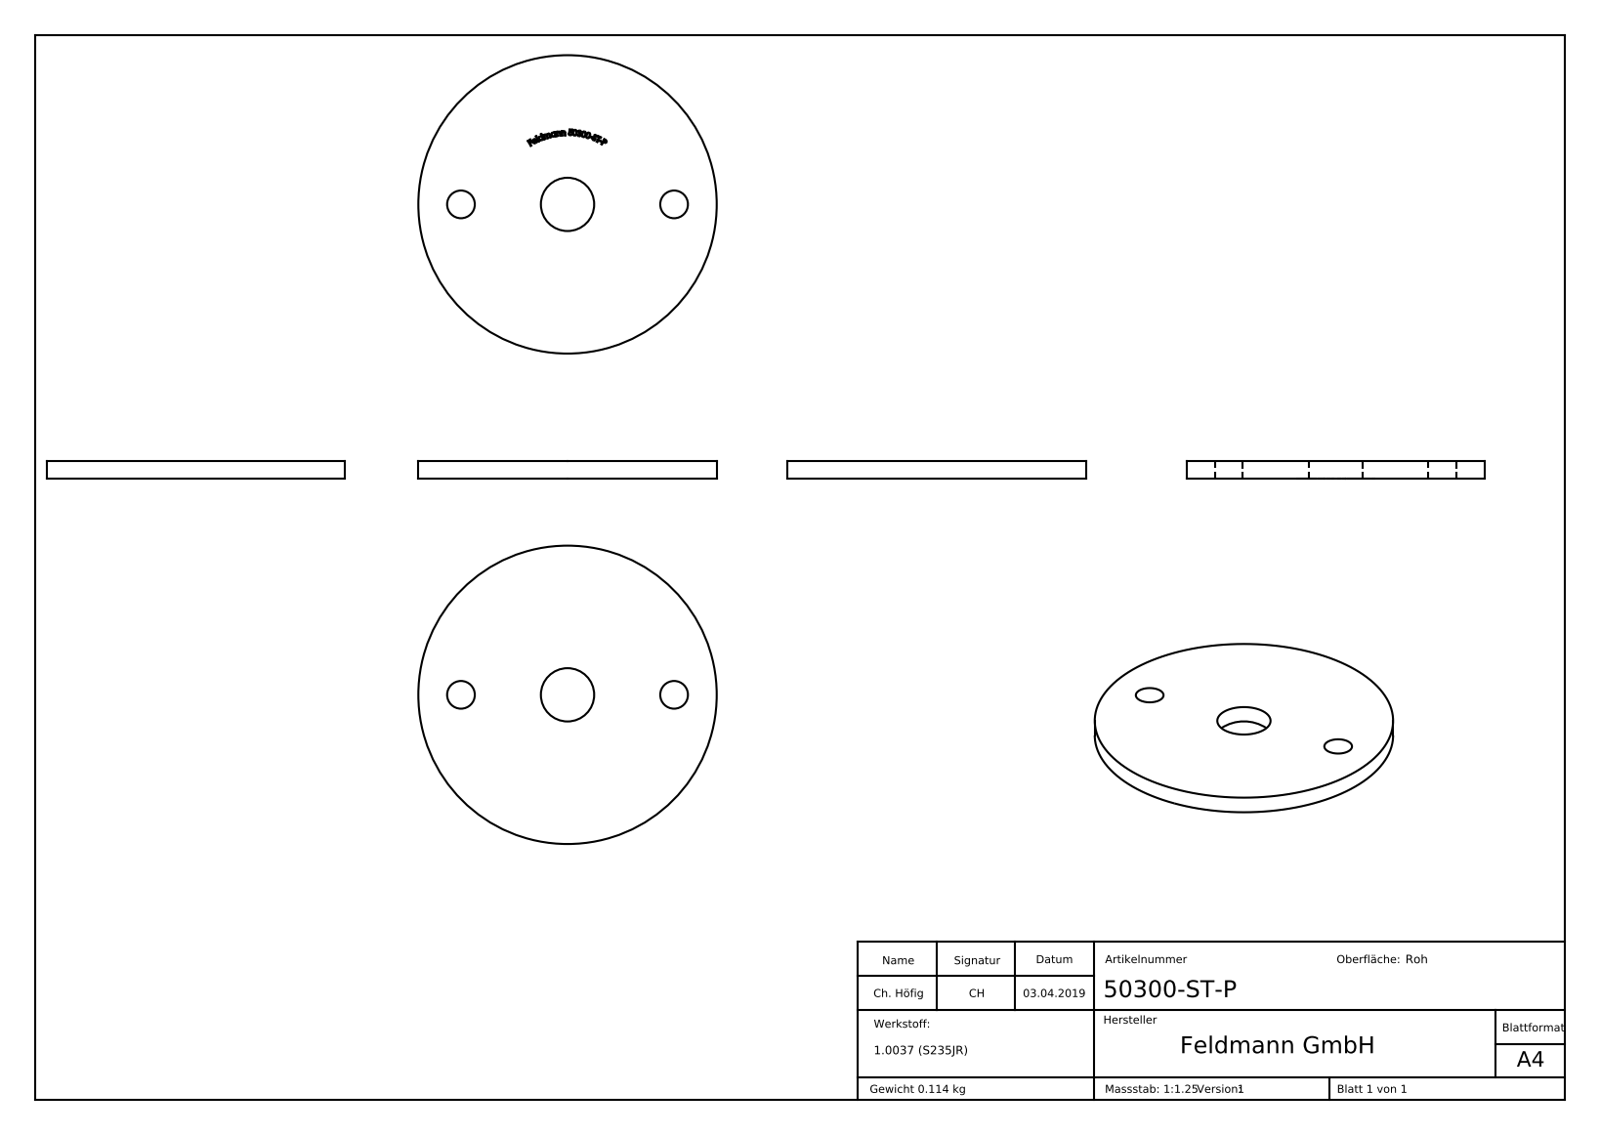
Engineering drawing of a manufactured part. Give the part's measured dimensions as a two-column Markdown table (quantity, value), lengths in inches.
| quantity | value |
| --- | --- |
| part name | 50300-ST-P |
| STEP written by | SolidWorks 2015 (CONFIG_CONTROL_DESIGN) |
| units | inches |
| bodies | 1 solid, 242 faces (116 planar, 8 cylindrical, 118 other) |
| overall size | 2.756 × 2.756 × 0.157 |
| volume | 0.893 in³ |
| surface area | 13.22 in² |
| round holes (diameter × count) | 0.256 × 2, 0.492 × 1 |
| round bosses / shafts (diameter × count) | 2.756 × 1 |
| main face-to-face distances | 0.157, 0.154, 0.028, 0.033, 0.026, 0.057, 0.052, 0.016, 0.021, 0.026 |
| hole center spacings | 0.984, 1.969 |
